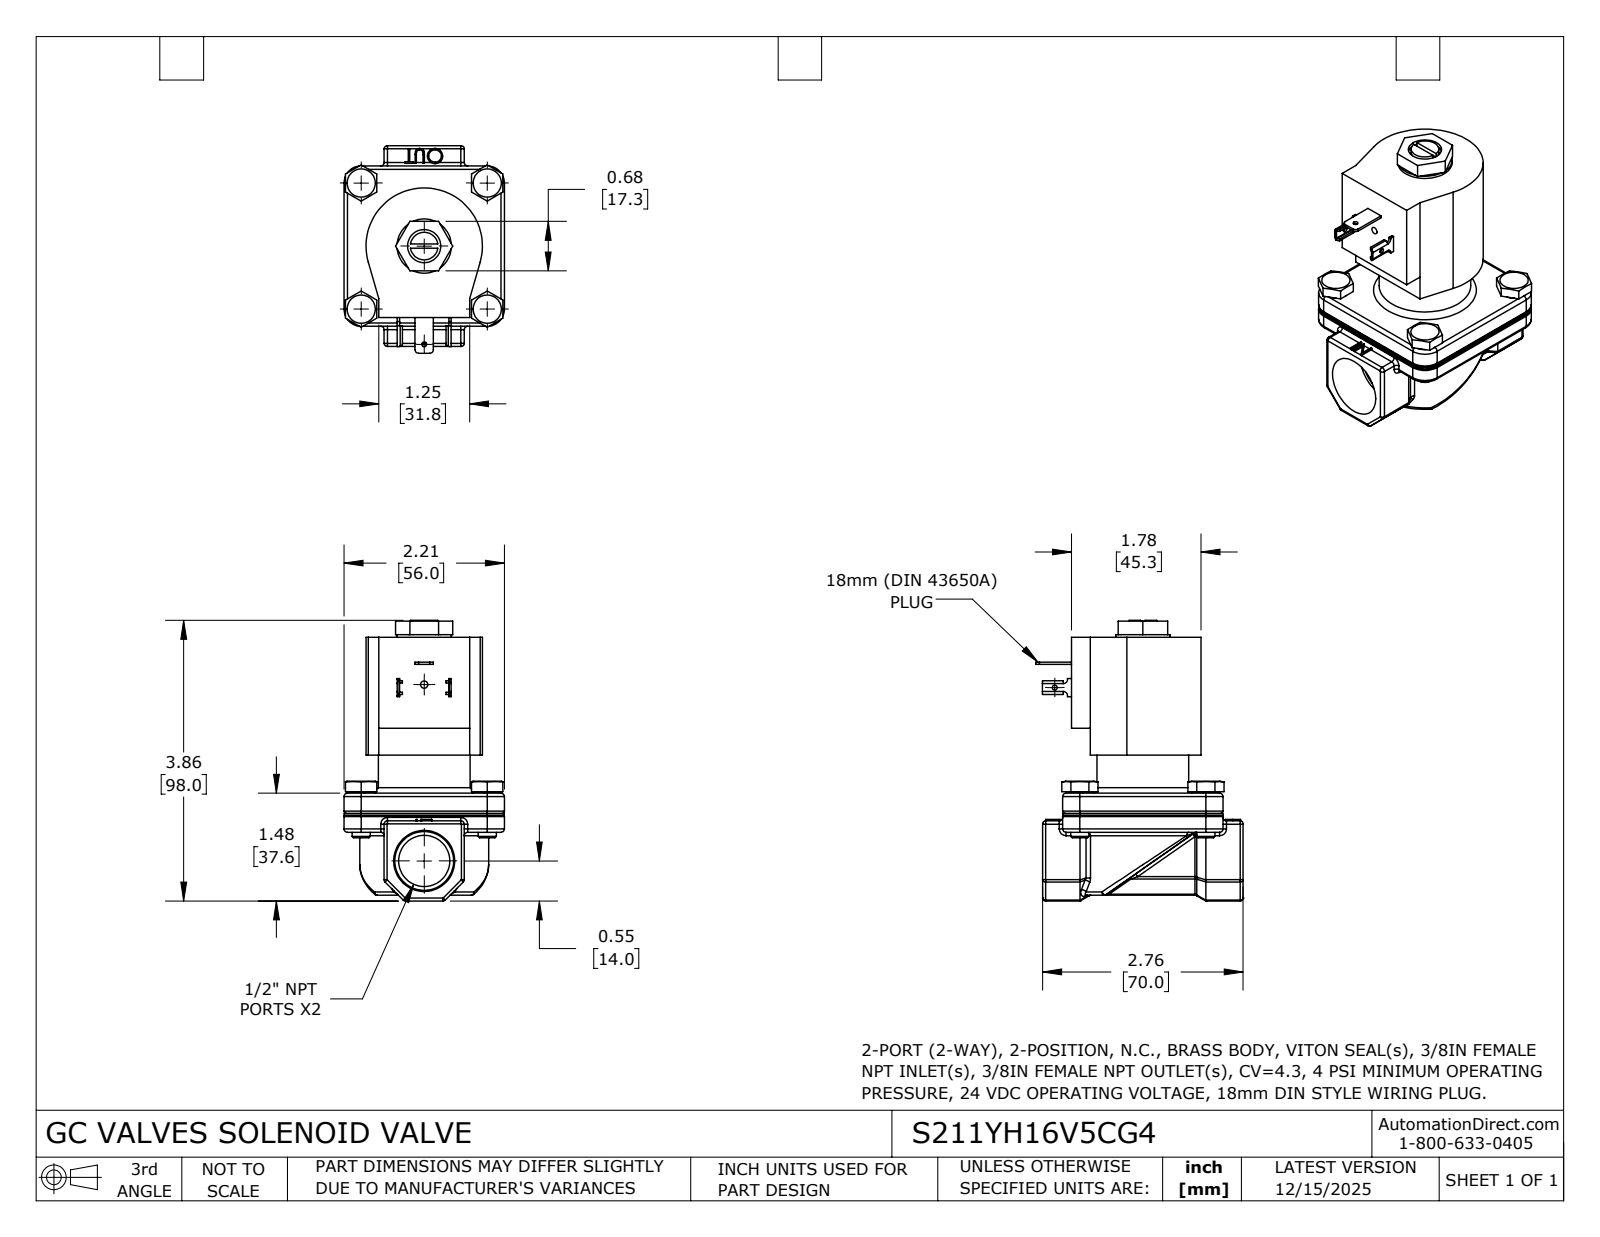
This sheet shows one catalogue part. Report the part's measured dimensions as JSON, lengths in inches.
{"part_name": "S211YH16V5CG4", "step_written_by": "SolidWorks 2024 (CONFIG_CONTROL_DESIGN)", "units": "inches", "bodies": {"solids": 1, "faces": 483, "planar": 204, "cylindrical": 153, "other": 126}, "overall_size": [3.857, 2.851, 2.205], "volume_in3": 9.336, "surface_area_in2": 41.74, "round_holes": [[0.066, 1], [0.067, 1], [0.1, 1], [0.456, 1], [0.703, 1]], "round_bosses_or_shafts": [[0.388, 4], [0.25, 4], [1.26, 1], [0.746, 1], [0.38, 1]], "partial_cylinders_radius": [[0.047, 57], [0.04, 12], [0.006, 4], [0.031, 4], [0.041, 4], [0.234, 4], [0.236, 4], [0.05, 2]], "face_to_face_distances": [2.143, 0.551, 1.654, 2.205, 0.537, 2.68, 0.276, 2.48, 1.06, 0.523], "hole_center_spacings": [1.35, 2.423]}
